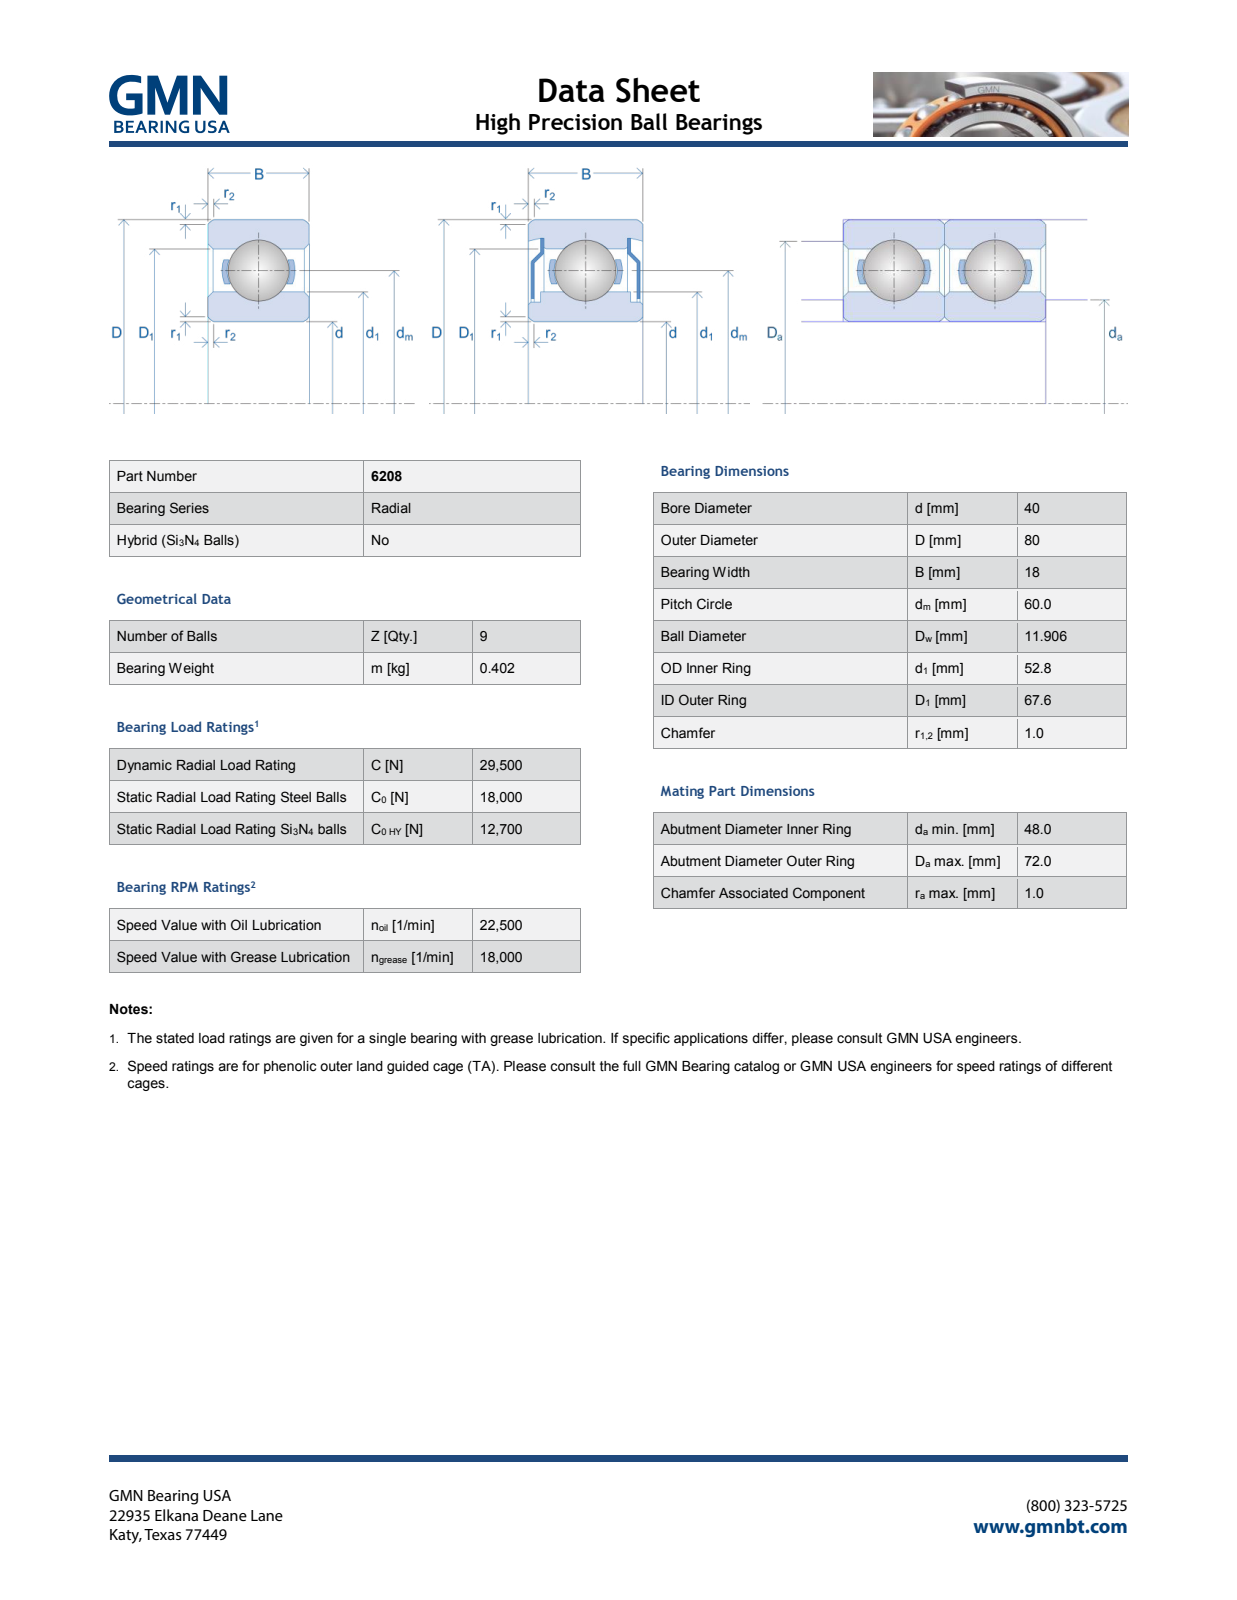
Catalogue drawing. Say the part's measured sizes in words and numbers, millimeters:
The part is named "6208_PRT". Its 3-D file was written by "PRO/ENGINEER BY PARAMETRIC TECHNOLOGY CORPORATION, 2013150 (AUTOMOTIVE_DESIGN)". It is 12 solids with 558 faces: 486 planar, 34 cylindrical and 38 other. Overall it measures 80 by 80 by 18.01 millimeters. Its volume is 53 513 cubic millimeters and its surface area 29 744 square millimeters. Round holes: 9 of diameter 12.11, 1 of diameter 40, 1 of diameter 59.6, 1 of diameter 67.6. Round bosses or shafts: 1 of diameter 80, 1 of diameter 66.8, 1 of diameter 52.8. The main face-to-face distances are 18, 17.9, 17.8, 17.91, 18.01, 0.47, 3.8, 0.48, 3.32, 0.4.
